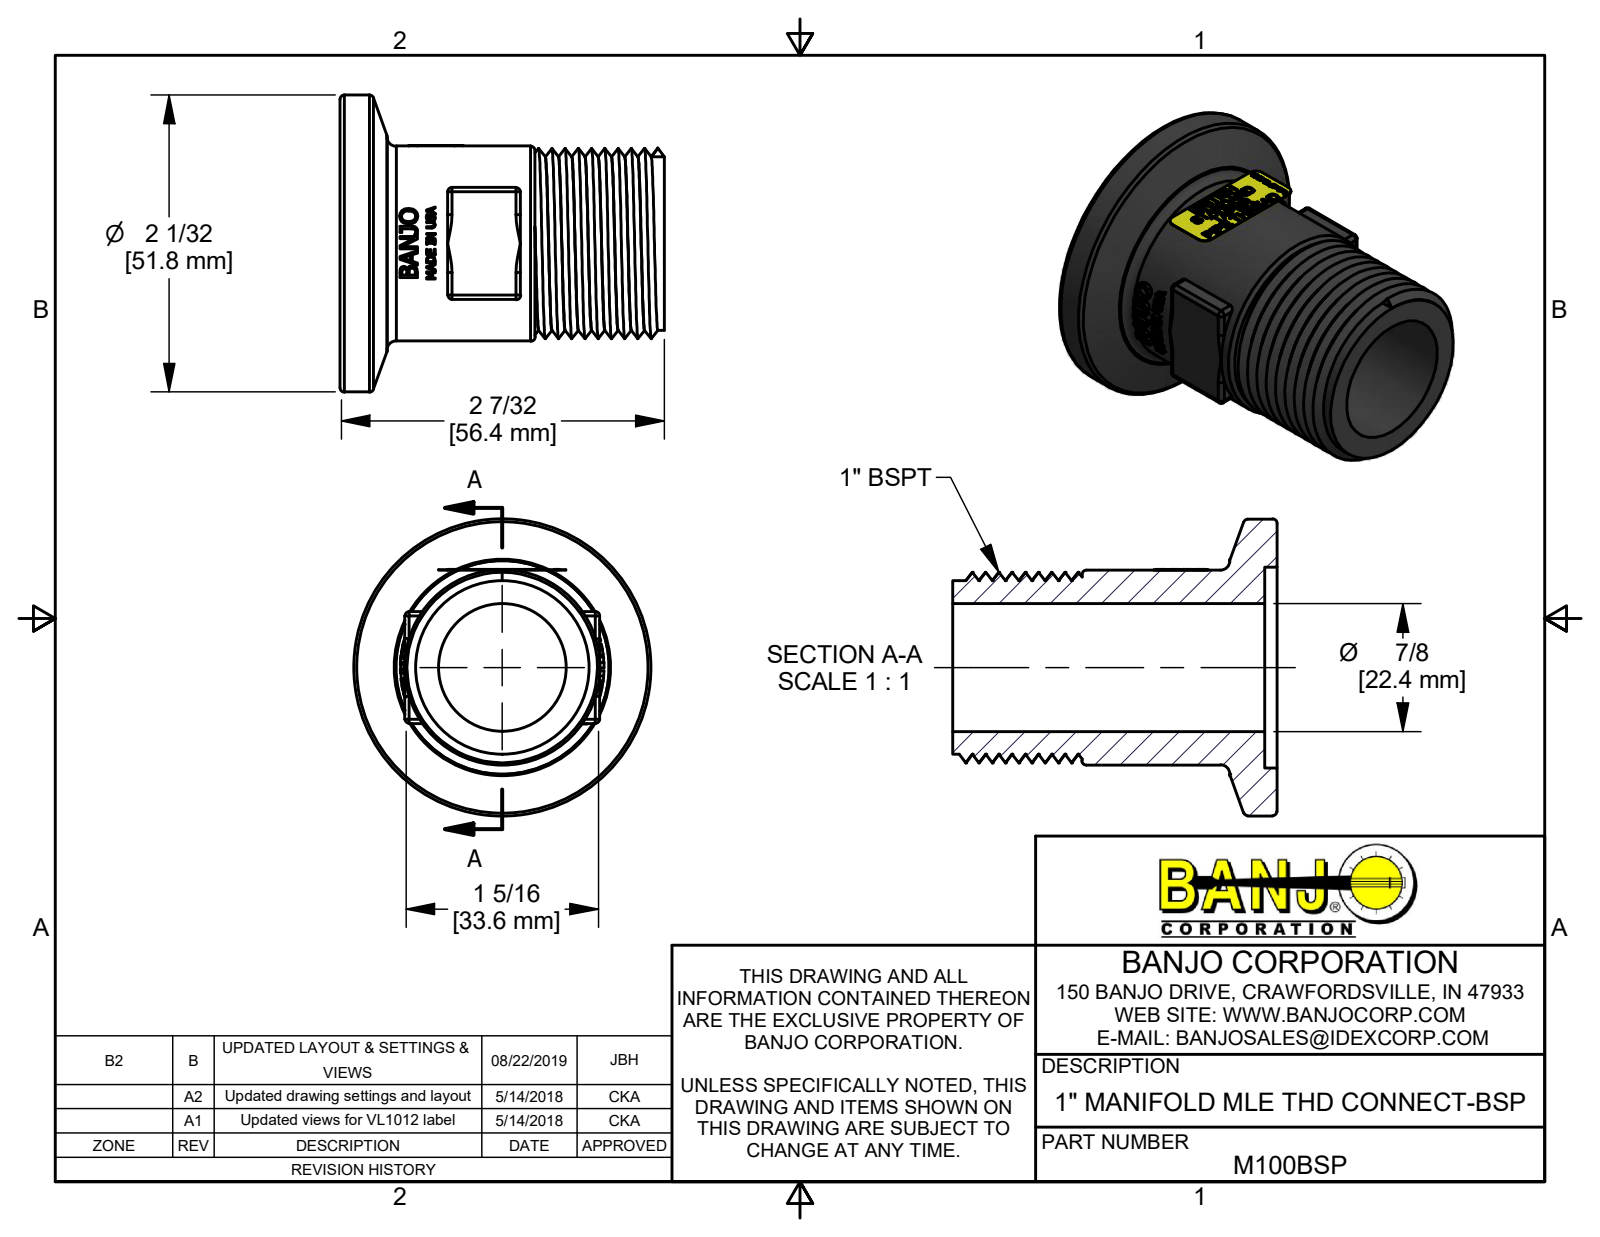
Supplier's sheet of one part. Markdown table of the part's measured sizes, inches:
| quantity | value |
| --- | --- |
| part name | M100BSP; M100BSPU; VL1012 |
| STEP written by | Autodesk Inventor 2019 (AUTOMOTIVE_DESIGN) |
| units | inches |
| bodies | 2 solids, 1011 faces (603 planar, 73 cylindrical, 335 other) |
| overall size | 2.23 × 2.04 × 2.04 |
| volume | 2.1 in³ |
| surface area | 23.83 in² |
| round holes (diameter × count) | 0.88 × 1, 1.38 × 1 |
| round bosses / shafts (diameter × count) | 2.04 × 1, 1.34 × 1, 1.193 × 1 |
| partial cylindrical surfaces (radius × count) | 0.03 × 12, 0.06 × 4, 0.7 × 1 |
| main face-to-face distances | 0.084, 2.146, 2.23, 1.34, 1.055, 1.058, 0.77, 0.285, 0.288, 0.89 |
